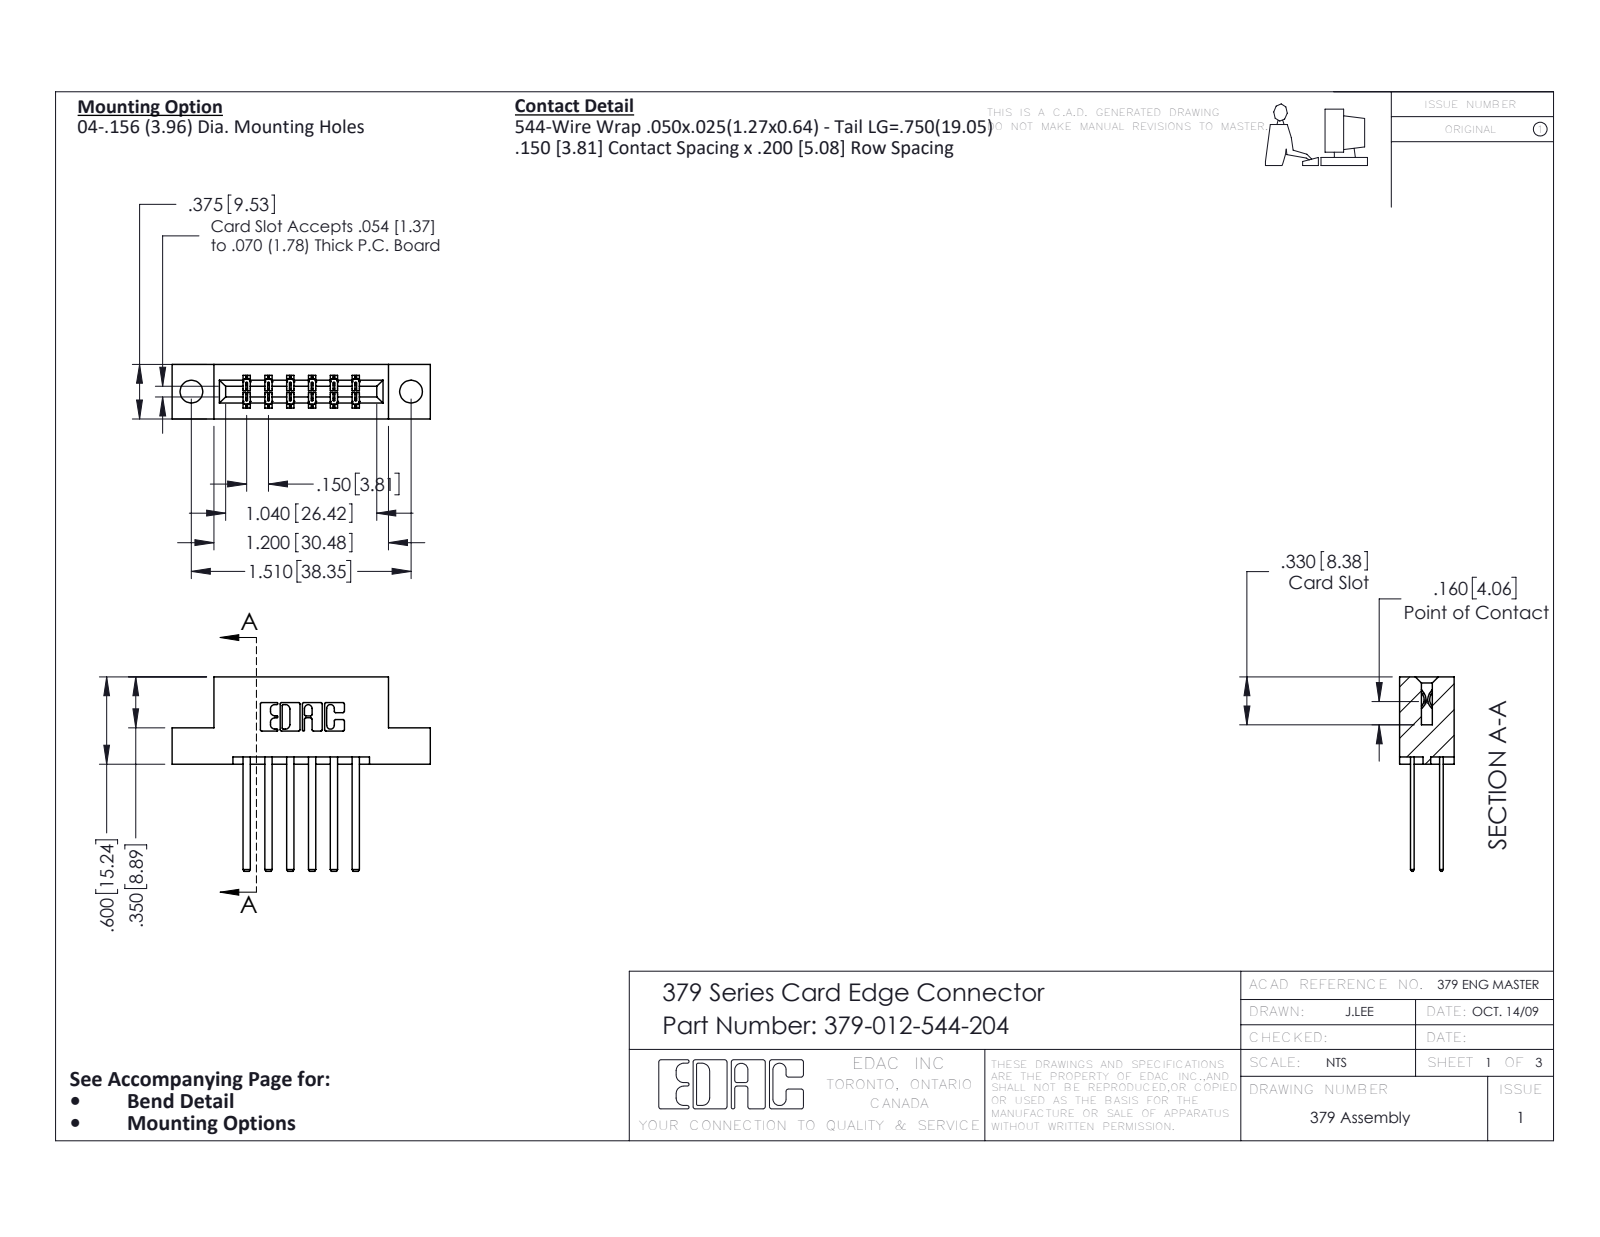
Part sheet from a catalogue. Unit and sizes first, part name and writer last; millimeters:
Units: millimetres
Overall size (bounding box): 45.1 × 34 × 9.5
Round holes (diameter × count): ⌀4 ×2
Partial cylindrical surfaces — rounded edges, fillets, slot ends (radius × count): R0.3 ×22, R0.2 ×18, R0.2 ×6, R0.8 ×6, R0.7 ×3, R0.4 ×2, R0.6 ×2, R0.6 ×2
Main face-to-face distances: 7.6, 5.1, 2.5, 3.8, 1.3, 6.4, 8.9, 1.9, 9.5, 14
Hole centre spacings: 38.4
Volume: 4 420 mm³ · Surface area: 4 990 mm²
Bodies: 13 solids, 666 faces (454 planar, 212 cylindrical, 0 other)
Part name (STEP PRODUCT): 345-292-001_345-293-144; 379-012-544-204; 379 Part_Flush - .156 Dia - TH
STEP written by: SolidWorks 2016 (CONFIG_CONTROL_DESIGN)
